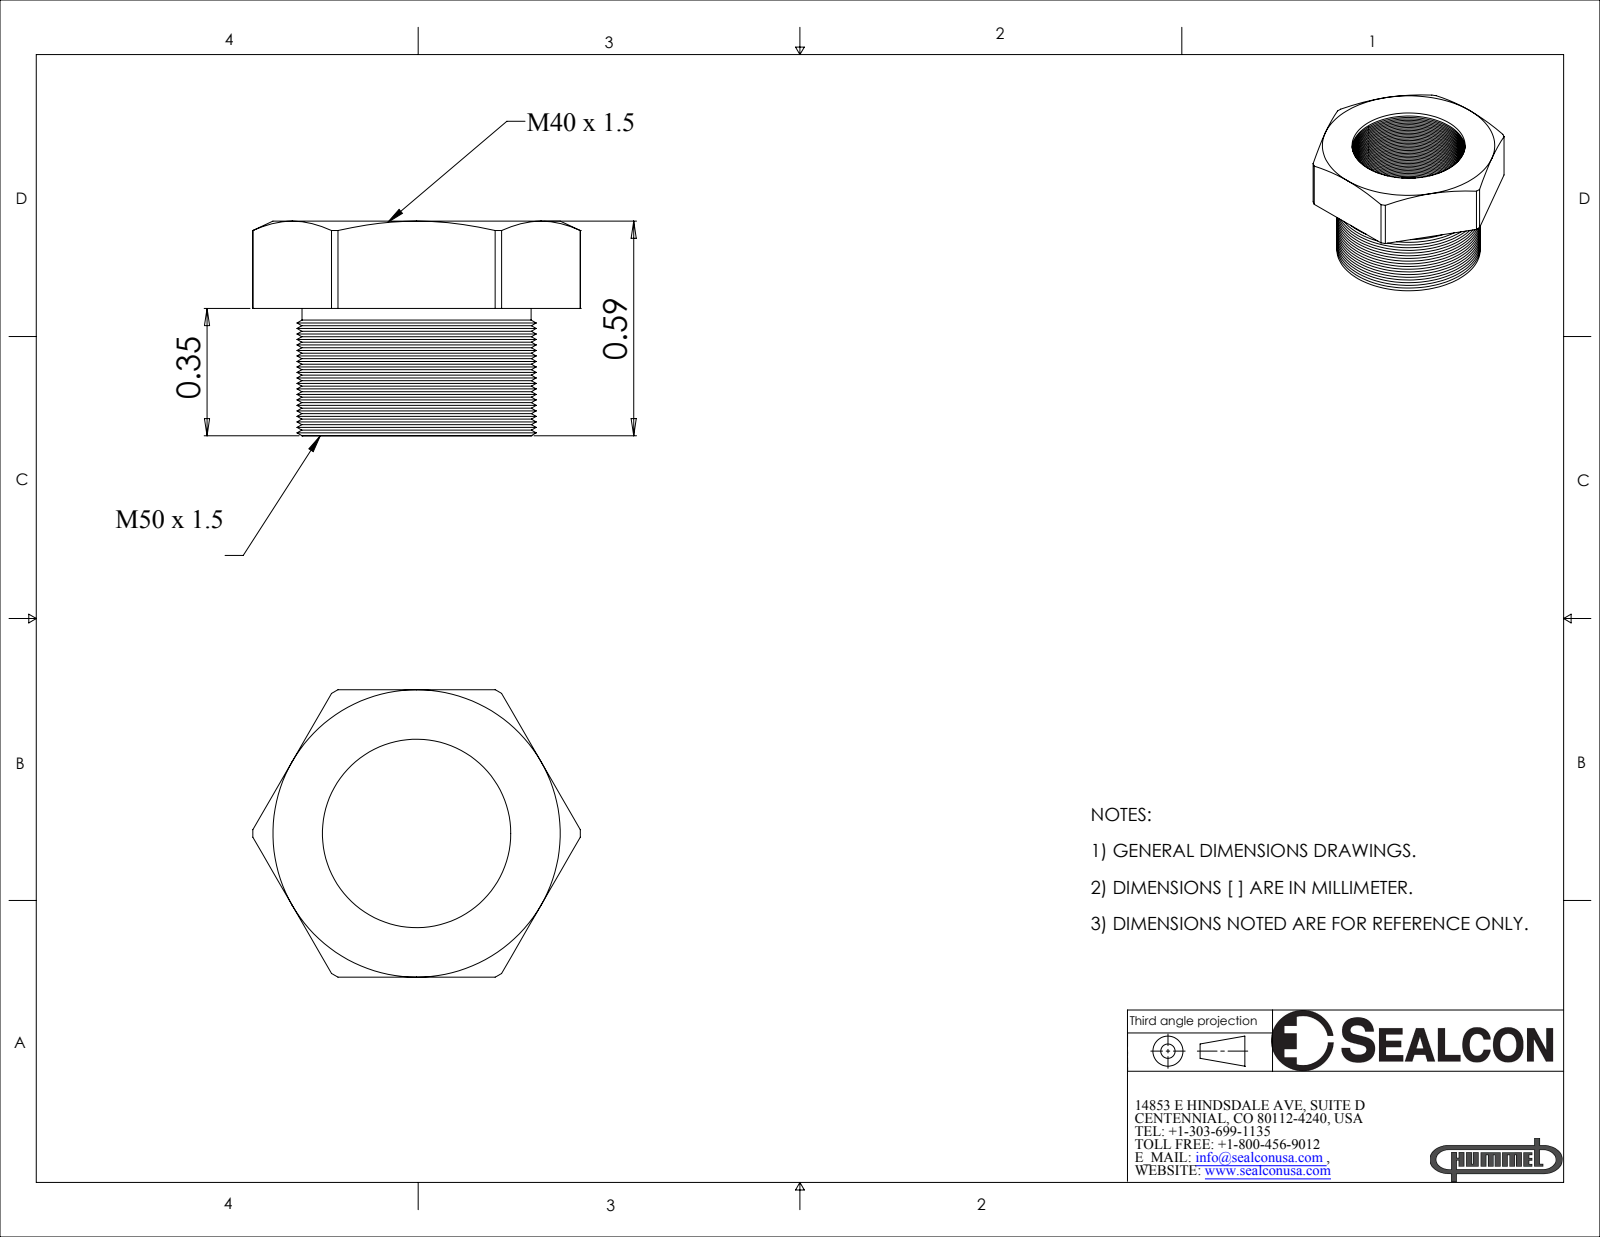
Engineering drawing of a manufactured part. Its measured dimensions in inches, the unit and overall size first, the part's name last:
Units: inches
Overall size (bounding box): 0.901 × 0.79 × 0.59
Round holes (diameter × count): ⌀0.518 ×1
Round bosses / shafts (diameter × count): ⌀0.63 ×1
Partial cylindrical surfaces — rounded edges, fillets, slot ends (radius × count): R0.45 ×1
Main face-to-face distances: 0.79, 0.24, 0.35, 0.59
Volume: 0.116 in³ · Surface area: 4.586 in²
Bodies: 1 solid, 329 faces (9 planar, 85 cylindrical, 235 other)
Part name (STEP PRODUCT): RM-5040-SS
STEP written by: SolidWorks 2008 (CONFIG_CONTROL_DESIGN)
